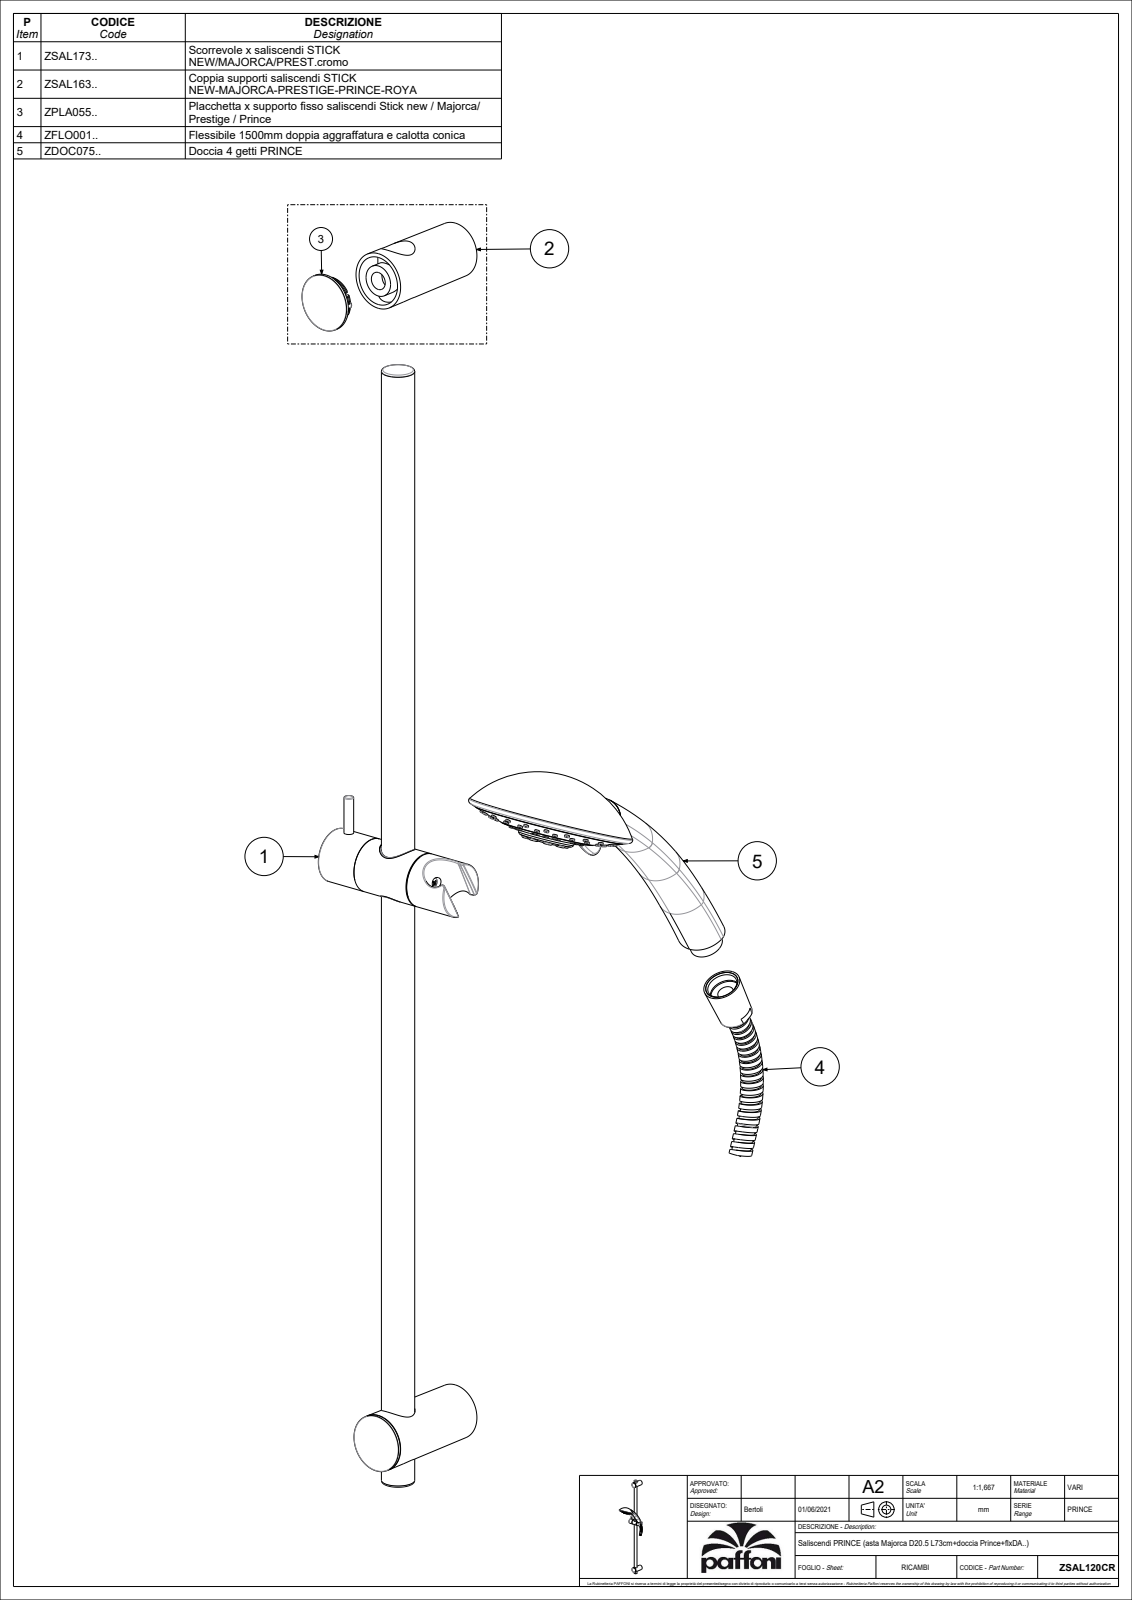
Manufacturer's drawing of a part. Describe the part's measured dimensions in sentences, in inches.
The part is named "ZSAL120CR". Its 3-D file was written by "CREO PARAMETRIC BY PTC INC, 2020044 (CONFIG_CONTROL_DESIGN)". It is 6 solids with 1047 faces: 237 planar, 449 cylindrical and 361 other. Overall it measures 28.898 by 10.358 by 5.683 inches. Its volume is 40.69 cubic inches and its surface area 301.1 square inches. Round holes: 39 of diameter 0.02, 15 of diameter 0.055, 8 of diameter 0.051, 3 of diameter 1.22, 2 of diameter 0.213, 2 of diameter 0.441, 2 of diameter 0.886, 1 of diameter 0.15, 1 of diameter 0.315, 1 of diameter 0.433, 1 of diameter 0.551, 1 of diameter 0.709. Round bosses or shafts: 39 of diameter 0.118, 2 of diameter 1.437, 2 of diameter 1.378, 2 of diameter 0.882, 2 of diameter 0.472, 1 of diameter 2.323, 1 of diameter 1.386, 1 of diameter 1.339. Partial cylindrical surfaces (rounded edges, fillets, slot ends): 30 of radius 0.049, 30 of radius 0.121, 11 of radius 0.059, 8 of radius 0.024, 8 of radius 0.118, 6 of radius 0.02, 4 of radius 0.012, 2 of radius 0.506. The main face-to-face distances are 0.043, 14.43, 14.473, 14.386, 0.079, 2.685, 2.764, 0.039, 2.913, 2.563. The hole center spacings are 0.333, 0.27, 1.61, 1.699, 0.333, 0.523, 0.781, 0.873.
